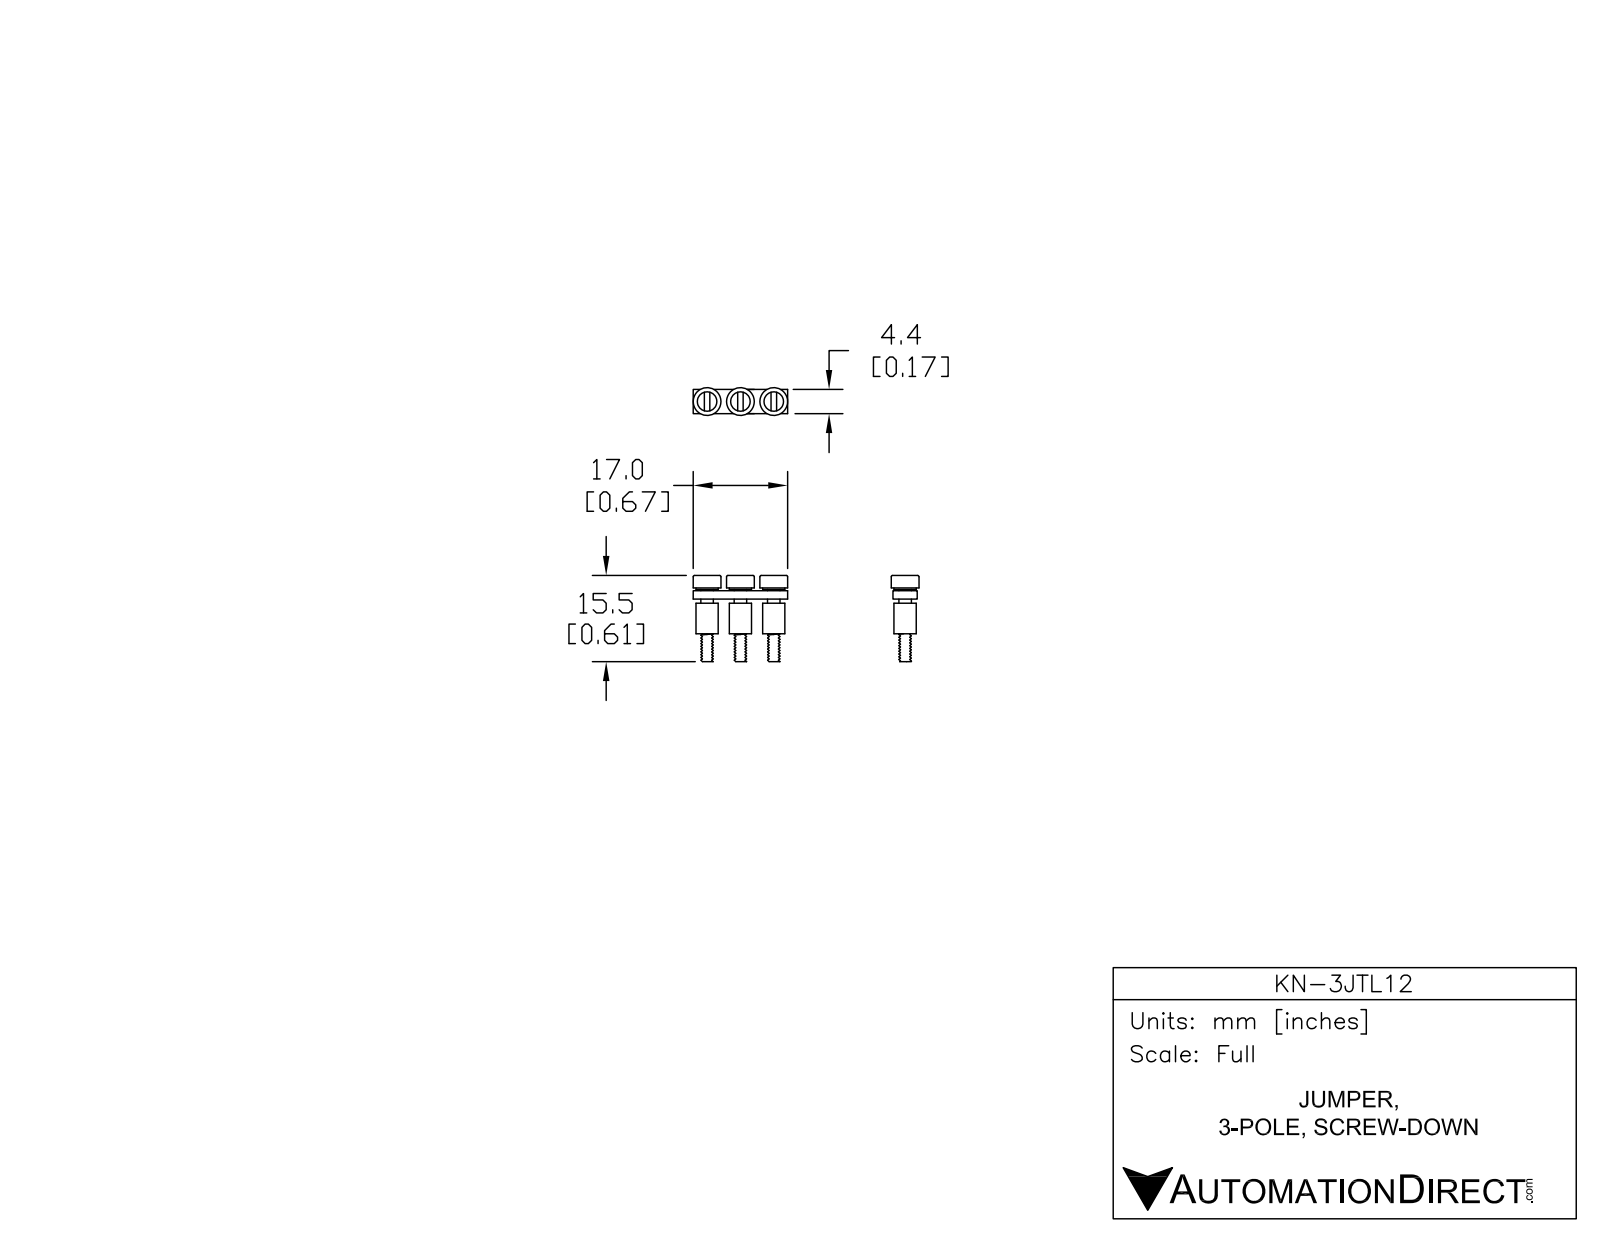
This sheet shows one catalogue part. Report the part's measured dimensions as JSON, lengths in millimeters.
{"part_name": "KN-3JTL12", "step_written_by": "SolidWorks 2014 (AUTOMOTIVE_DESIGN)", "units": "millimeters", "bodies": {"solids": 10, "faces": 102, "planar": 45, "cylindrical": 39, "other": 18}, "overall_size": [17, 15.5, 5], "volume_mm3": 472, "surface_area_mm2": 1313, "round_holes": [[3, 3], [3.5, 3]], "round_bosses_or_shafts": [[5, 3], [4, 3], [2.25, 3]], "face_to_face_distances": [1.5, 2, 2.25, 1.75, 0.5, 2.75, 2.5, 1, 5, 0.75], "hole_center_spacings": [6, 12]}
